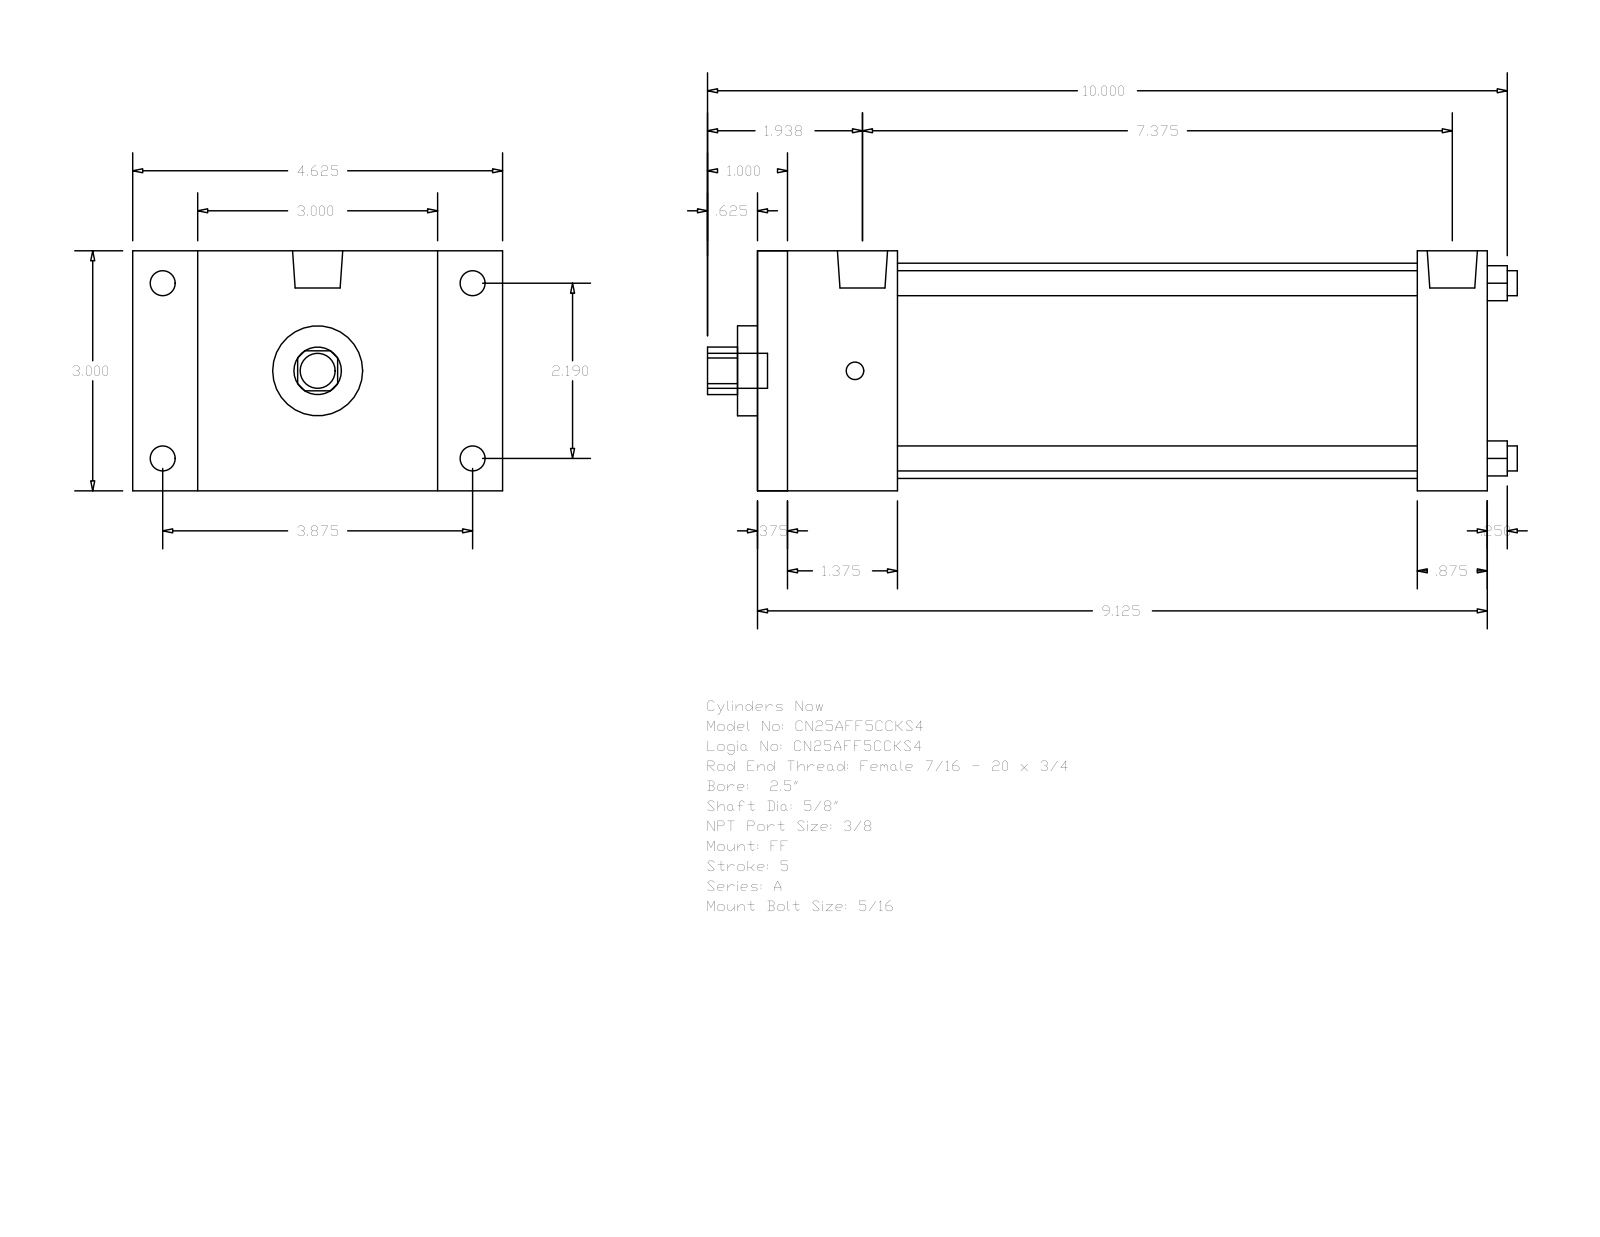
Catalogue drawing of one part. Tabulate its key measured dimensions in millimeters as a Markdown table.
| quantity | value |
| --- | --- |
| part name | A_FF__0250_0.625 |
| STEP written by | GSSL Pune (CONFIG_CONTROL_DESIGN) |
| units | millimeters |
| bodies | 0 solids, 92 faces (64 planar, 28 cylindrical, 0 other) |
| overall size | 257.18 × 117.47 × 76.2 |
| round holes (diameter × count) | 7.94 × 4, 15.88 × 1, 28.57 × 1, 68.33 × 1 |
| round bosses / shafts (diameter × count) | 7.94 × 4, 5.56 × 4, 15.93 × 2, 11.11 × 1 |
| partial cylindrical surfaces (radius × count) | 7.54 × 1 |
| main face-to-face distances | 76.2, 231.77, 9.52, 222.25, 44.45, 209.55, 34.93, 200.03, 165.1, 187.32 |
| hole center spacings | 39.33, 55.62, 78.66 |
